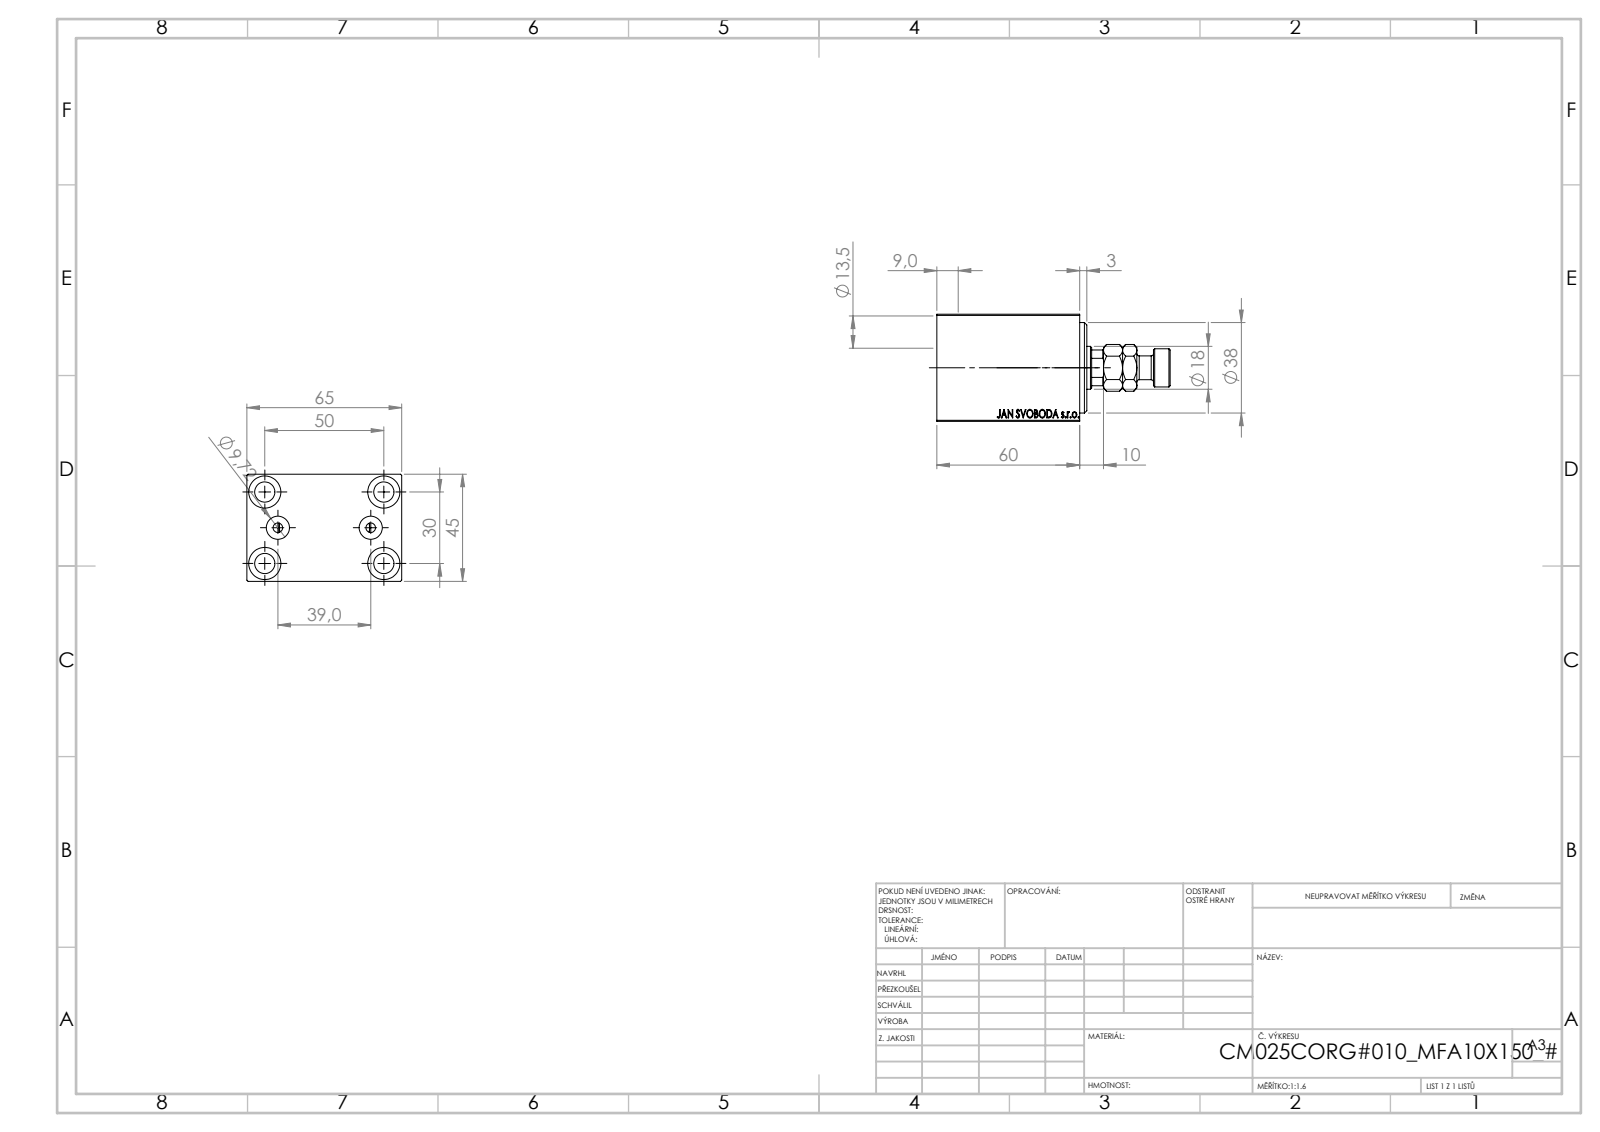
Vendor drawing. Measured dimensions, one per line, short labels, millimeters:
name: MFA; V450CM_C_VCP; V450CM_C_Body; V450CM_VC_B
written by: SolidWorks 2019 (CONFIG_CONTROL_DESIGN)
unit: mm
bodies: 4 solids, 910 faces (424 planar, 60 cylindrical, 426 other)
size: 98 × 65 × 45
volume: 159 803 mm³; area: 44 929 mm²
holes: 5× ⌀8.5, 4× ⌀13.5, 2× ⌀4, 2× ⌀9.72, 1× ⌀18, 1× ⌀21.5, 1× ⌀25, 1× ⌀27, 1× ⌀38
bosses: 1× ⌀16, 1× ⌀10
rounds: 1× R8.5
face distances: 45, 65, 9, 51, 60, 55, 5, 46, 10, 3
hole spacings: 15.98, 29.15, 46.96, 19.5, 30, 50, 58.31, 39
